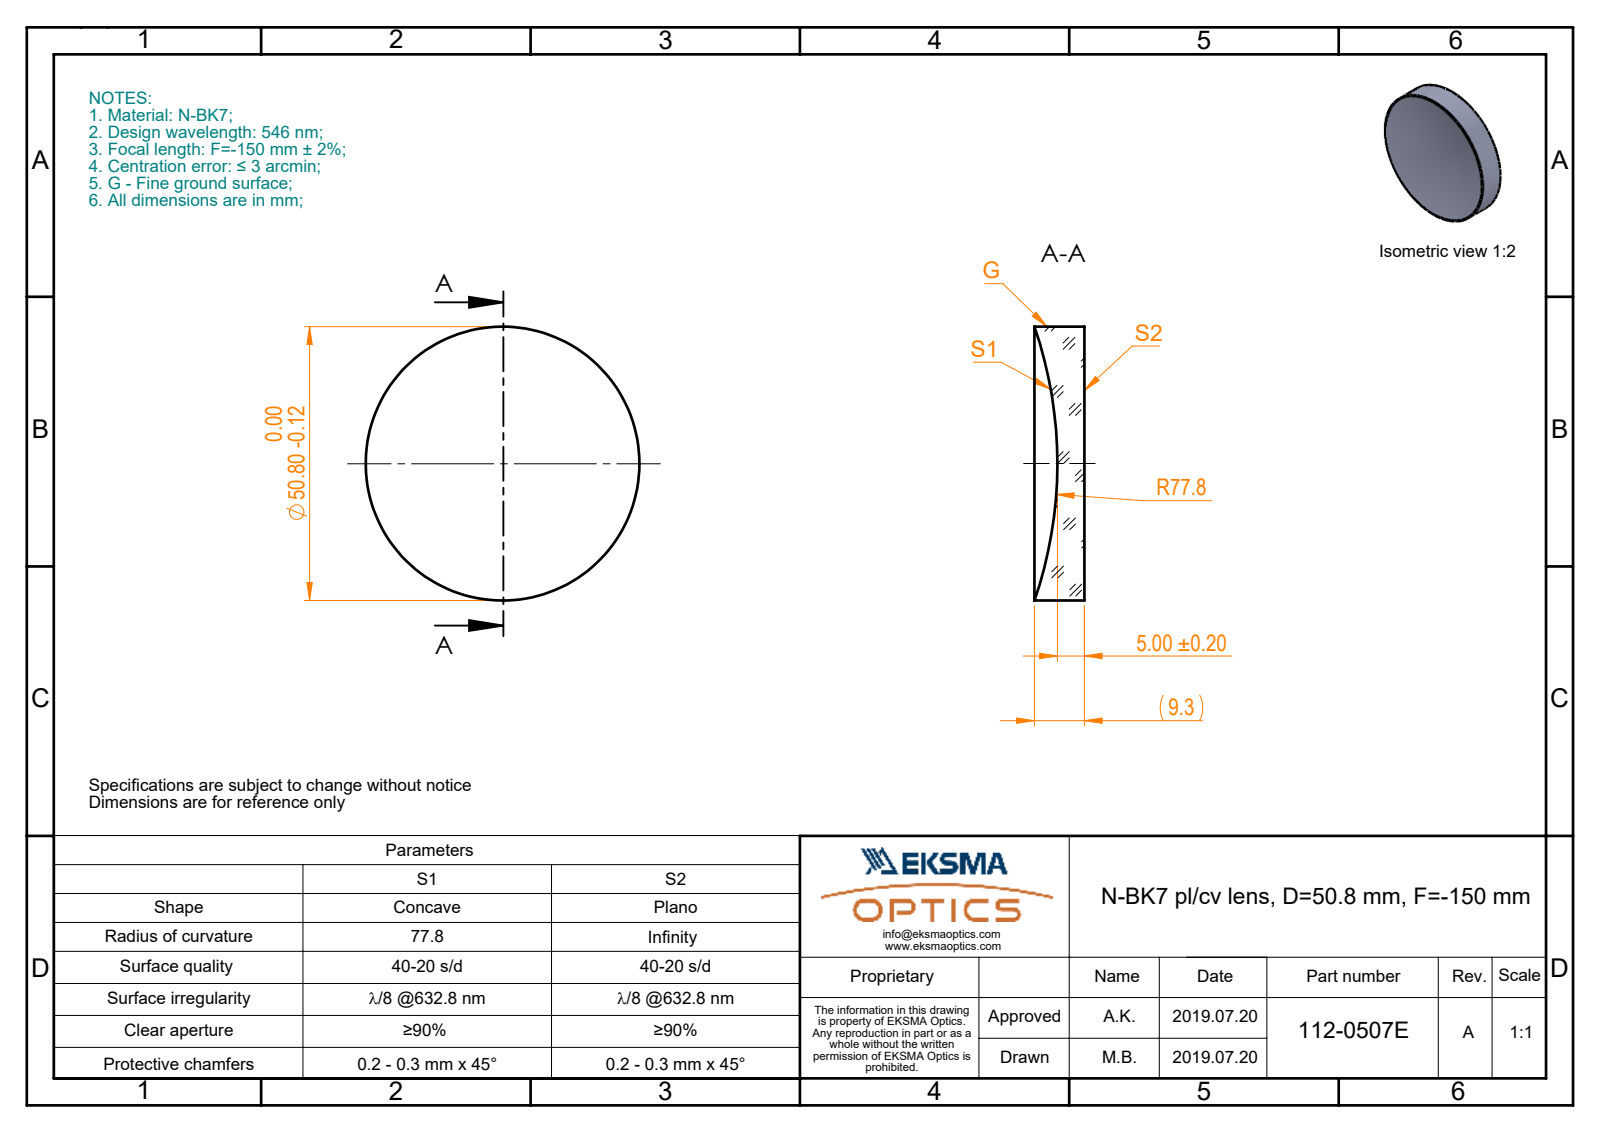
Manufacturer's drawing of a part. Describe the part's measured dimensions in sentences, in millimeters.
The part is named "112-0507 BK7 pl-cv 50.8 F-150". Its 3-D file was written by "SolidWorks 2017 (CONFIG_CONTROL_DESIGN)". It is 1 solid with 5 faces: 1 planar, 2 cylindrical and 2 other. Overall it measures 50.8 by 50.8 by 9.26 millimeters. Its volume is 14 413 cubic millimeters and its surface area 5 589 square millimeters. Round bosses or shafts: 1 of diameter 50.8.
